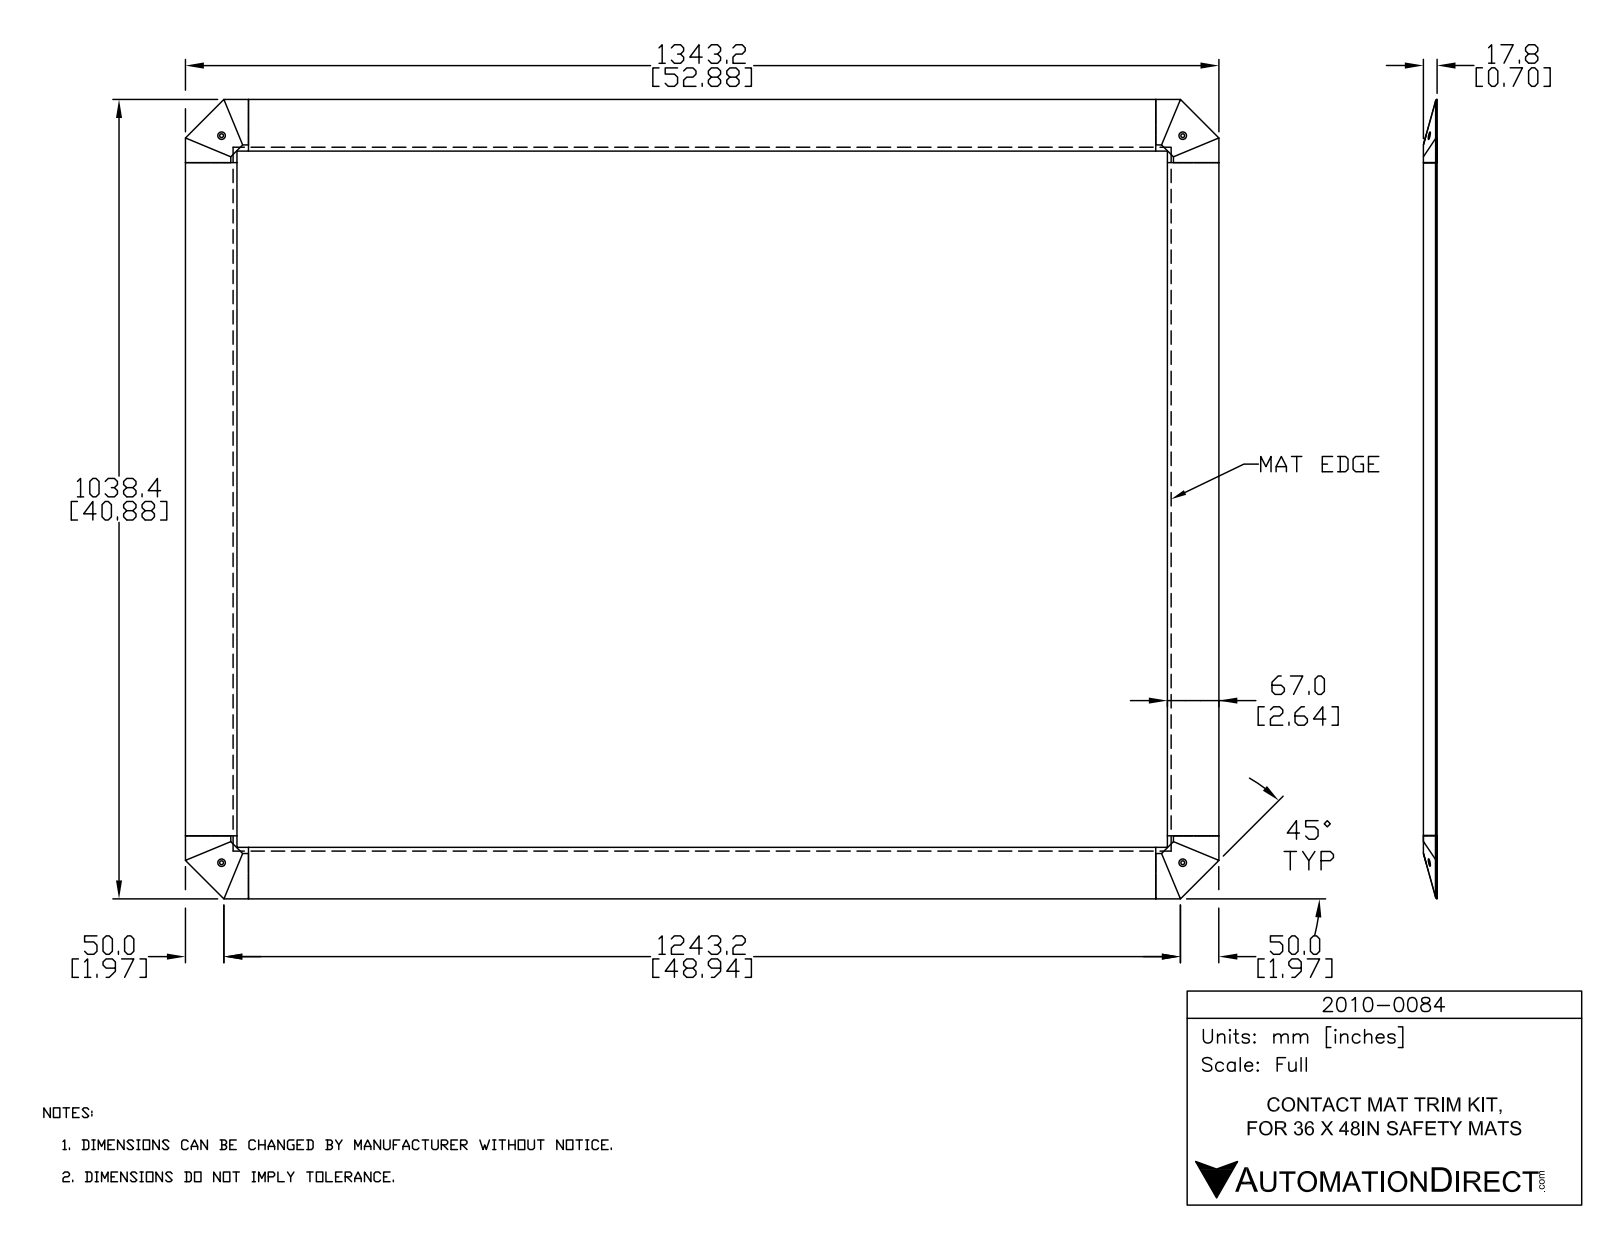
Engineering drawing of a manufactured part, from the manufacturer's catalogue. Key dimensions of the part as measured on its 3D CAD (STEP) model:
Part name (STEP PRODUCT): 2010-0084
STEP written by: SolidWorks 2018 (AUTOMOTIVE_DESIGN)
Units: inches
Bodies: 1 solid, 2109 faces (1613 planar, 440 cylindrical, 56 other)
Overall size (bounding box): 52.882 × 40.882 × 0.701
Volume: 78.56 in³ · Surface area: 1 548 in²
Round holes (diameter × count): ⌀0.197 ×4, ⌀0.386 ×4
Round bosses / shafts (diameter × count): ⌀0.394 ×4
Partial cylindrical surfaces — rounded edges, fillets, slot ends (radius × count): R0.008 ×200, R0.039 ×108, R0.02 ×60, R0.017 ×8, R0.512 ×8, R0.291 ×4, R0.394 ×4
Main face-to-face distances: 0.114, 0.076, 0.19, 0.038, 0.118, 0.63, 0.079, 0.304, 0.038, 0.748
Hole centre spacings: 37.181, 49.181, 61.654
